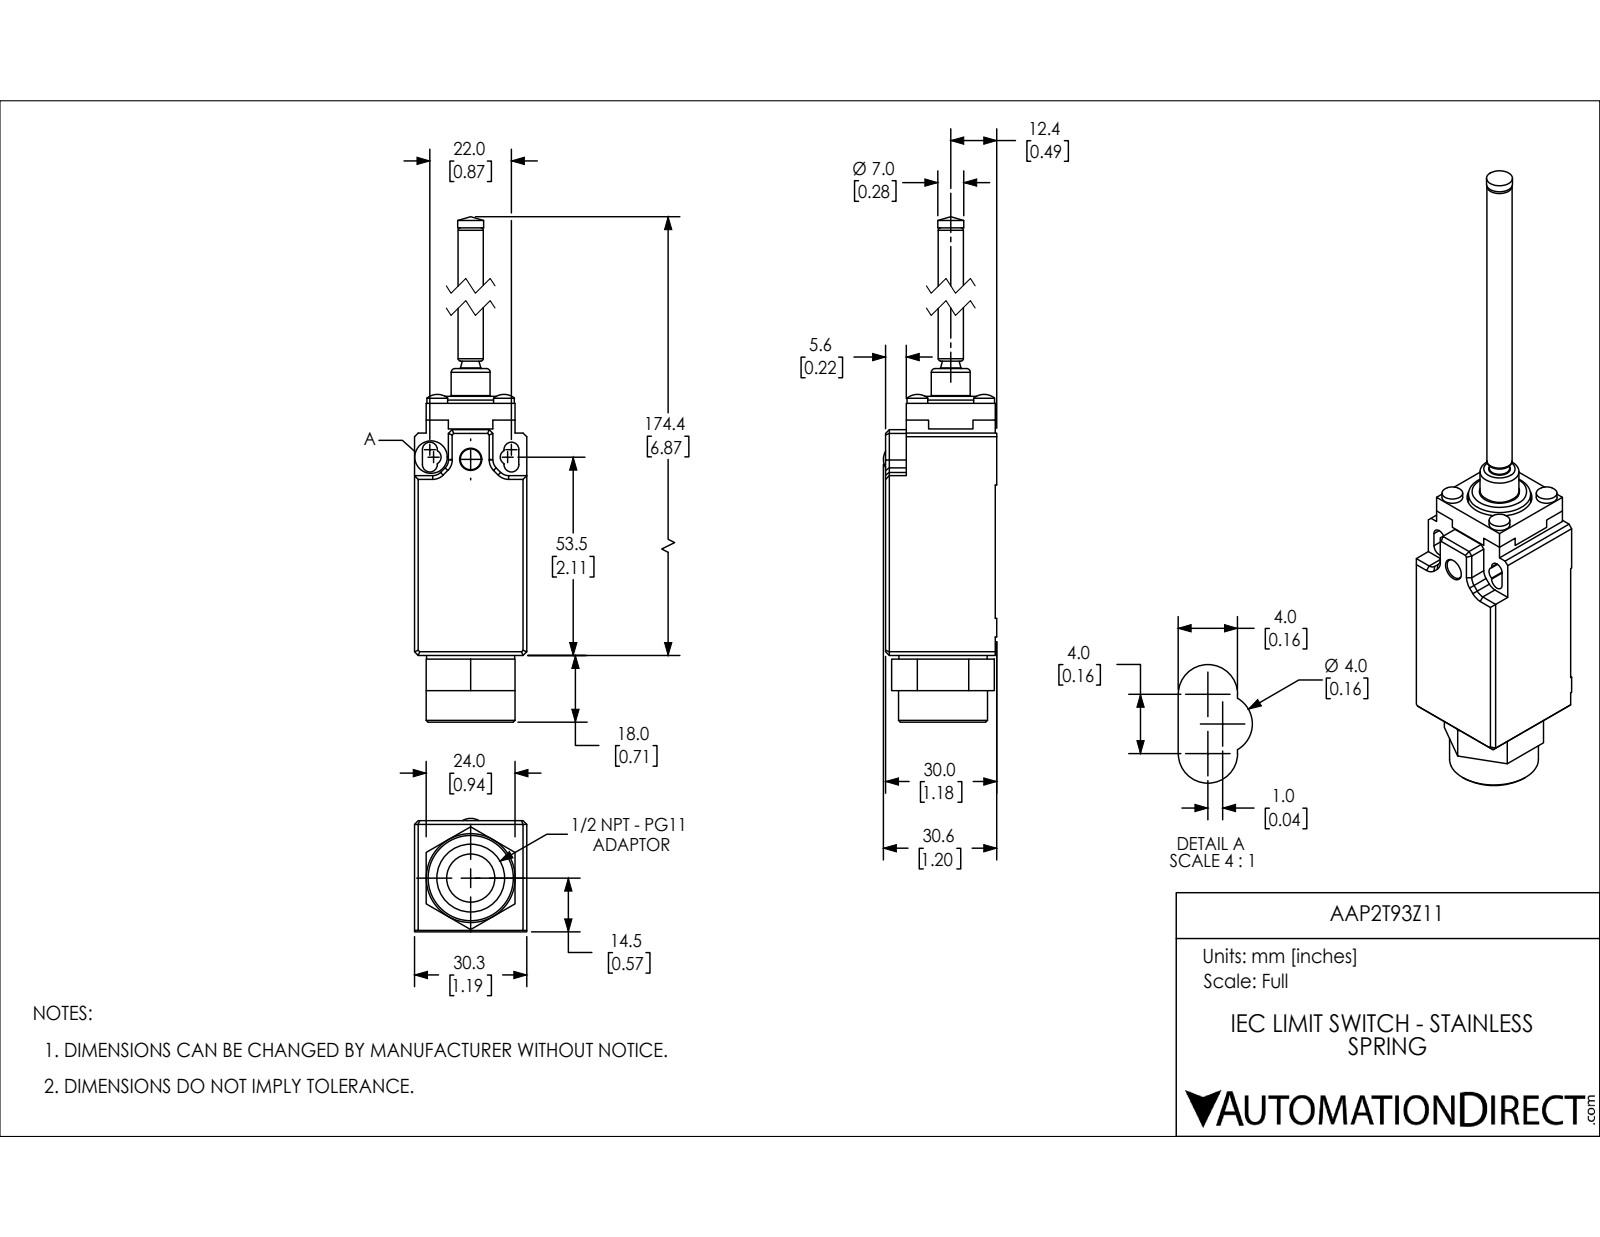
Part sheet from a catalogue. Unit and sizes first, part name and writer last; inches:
Units: inches
Overall size (bounding box): 7.575 × 1.205 × 1.193
Round holes (diameter × count): ⌀0.236 ×1, ⌀0.512 ×1, ⌀0.669 ×1, ⌀0.689 ×1, ⌀0.72 ×1, ⌀0.74 ×1, ⌀0.748 ×1
Round bosses / shafts (diameter × count): ⌀0.22 ×5, ⌀0.945 ×1, ⌀0.937 ×1, ⌀0.724 ×1, ⌀0.661 ×1, ⌀0.413 ×1, ⌀0.276 ×1, ⌀0.268 ×1
Partial cylindrical surfaces — rounded edges, fillets, slot ends (radius × count): R0.079 ×6, R0.118 ×4, R0.394 ×1, R0.4 ×1
Main face-to-face distances: 1.193, 1.165, 0.945, 0.039, 2.406, 0.124, 1.069, 0.016, 1.181, 0.236
Hole centre spacings: 0.083
Volume: 3.924 in³ · Surface area: 29.75 in²
Bodies: 5 solids, 206 faces (106 planar, 61 cylindrical, 39 other)
Part name (STEP PRODUCT): AAP2T93Z11
STEP written by: SolidWorks 2018 (AUTOMOTIVE_DESIGN)
